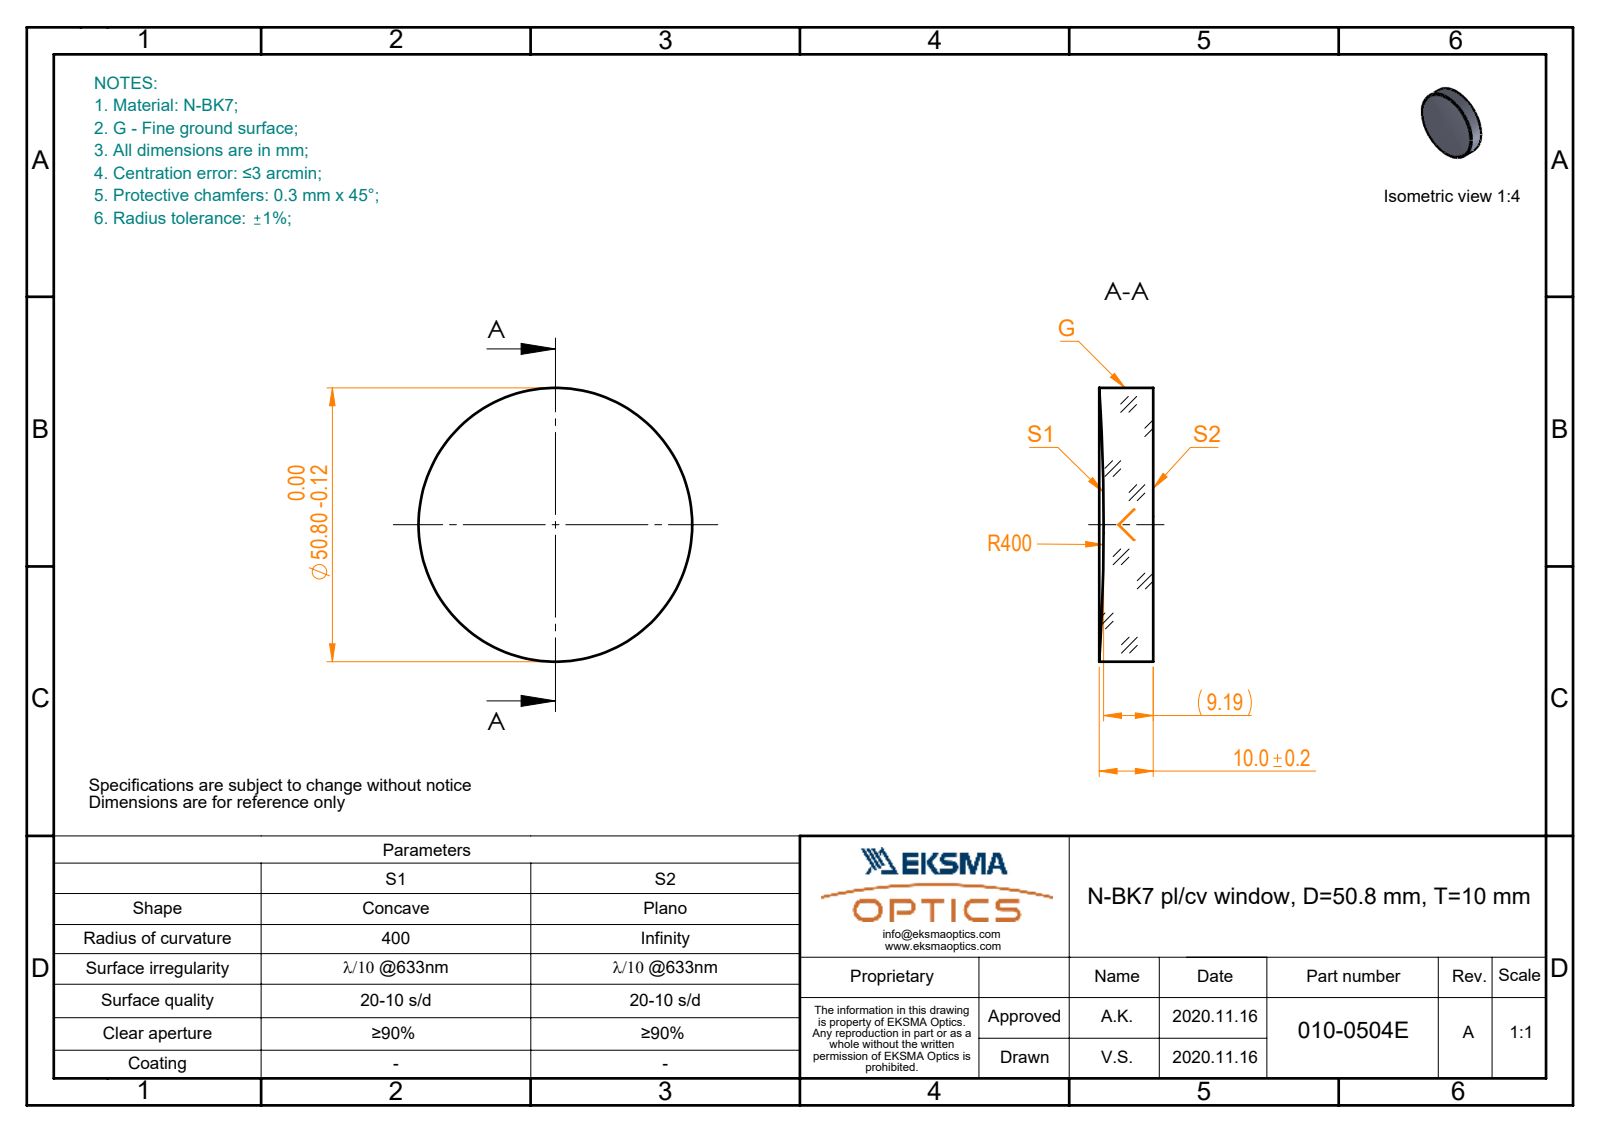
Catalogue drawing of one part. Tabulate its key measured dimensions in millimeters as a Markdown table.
| quantity | value |
| --- | --- |
| part name | 010-0504E_N-BK7_PCV_window |
| STEP written by | SolidWorks 2019 (CONFIG_CONTROL_DESIGN) |
| units | millimeters |
| bodies | 1 solid, 5 faces (1 planar, 2 cylindrical, 2 other) |
| overall size | 50.8 × 50.8 × 10 |
| volume | 19 450 mm³ |
| surface area | 5 652 mm² |
| round bosses / shafts (diameter × count) | 50.8 × 1 |
